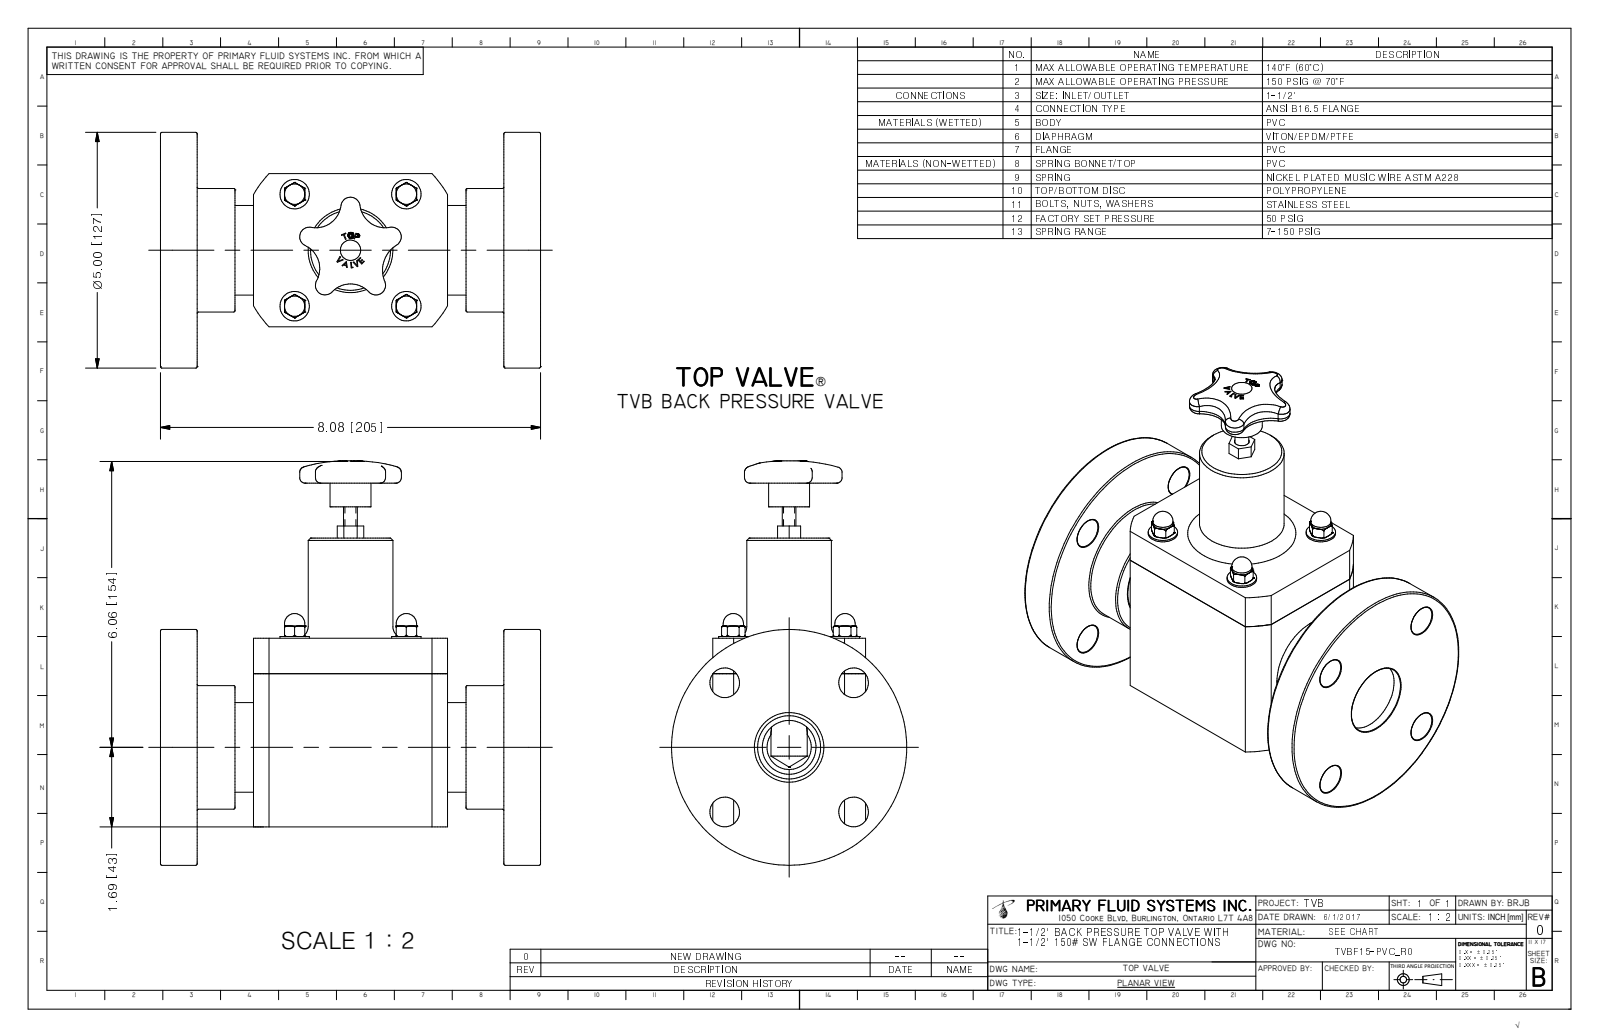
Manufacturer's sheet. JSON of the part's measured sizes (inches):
{"part_name": "TVBF15-PVC_R0", "step_written_by": "Autodesk Inventor 2009 (AUTOMOTIVE_DESIGN)", "units": "inches", "bodies": {"solids": 1, "faces": 393, "planar": 152, "cylindrical": 61, "other": 180}, "overall_size": [8.575, 8.08, 5], "volume_in3": 88.75, "surface_area_in2": 280.5, "round_holes": [[0.175, 4], [0.63, 4], [1.476, 1], [1.5, 1]], "round_bosses_or_shafts": [[0.625, 4], [0.433, 4], [0.375, 4], [5, 1], [2.62, 1], [1.9, 1], [1.8, 1], [0.87, 1]], "partial_cylinders_radius": [[0.085, 5], [0.205, 5], [0.536, 4], [0.656, 4], [0.625, 1], [0.745, 1], [2.375, 1]], "face_to_face_distances": [0.78, 7.3, 8.08, 3.25, 1.978, 6.103, 1.197, 5.322, 6.52, 4], "hole_center_spacings": [1.937, 2.74, 2.375, 2.375, 3.359, 3.875]}
